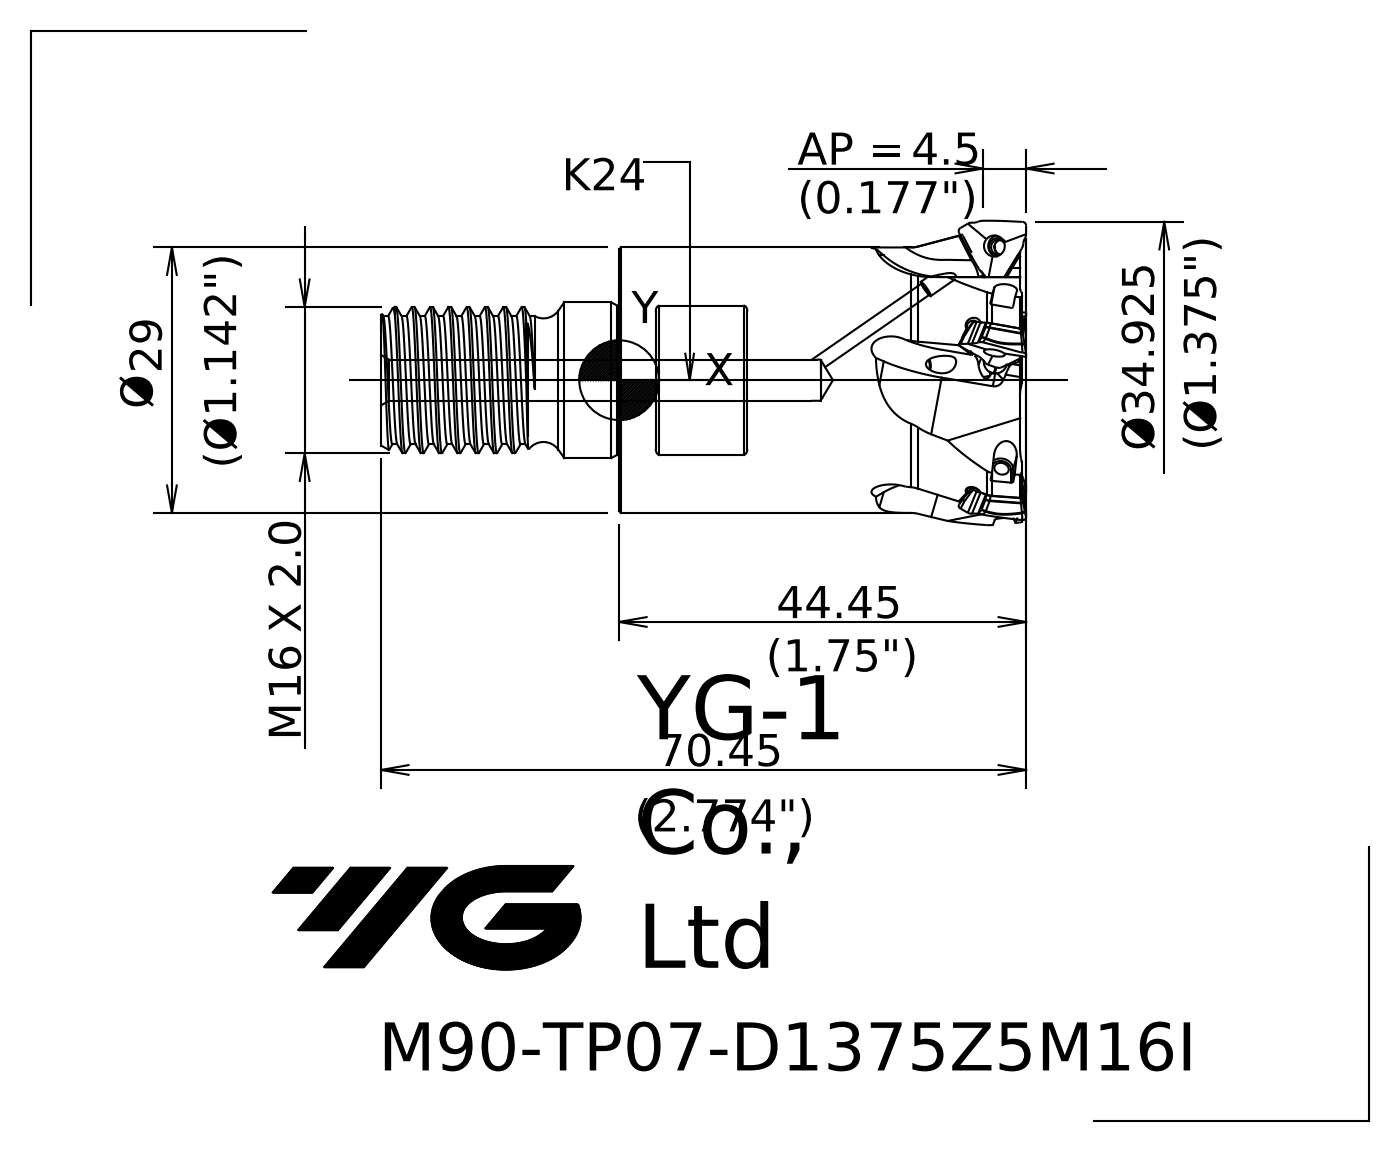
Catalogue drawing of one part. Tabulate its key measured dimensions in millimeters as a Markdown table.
| quantity | value |
| --- | --- |
| part name | 10224E48880365a2 |
| STEP written by | SIEMENS PLM Software NX 10.0 (AP203_CONFIGURATION_CONTROLLED_3D_DESIGN_OF_MECHANICAL_PARTS_AND_ASSEMBLIES_MIM_LF) |
| units | millimeters |
| bodies | 1 solid, 63 faces (11 planar, 10 cylindrical, 42 other) |
| overall size | 70.45 × 34.98 × 34.98 |
| volume | 33 908 mm³ |
| surface area | 10 204 mm² |
| round holes (diameter × count) | 1.5 × 1, 4.5 × 1 |
| round bosses / shafts (diameter × count) | 29 × 1, 17 × 1, 16 × 1, 14 × 1 |
| partial cylindrical surfaces (radius × count) | 0.4 × 4 |
| main face-to-face distances | 43.8, 24, 69.8, 26, 43.95, 69.95, 39.95, 39.8, 4, 30 |
